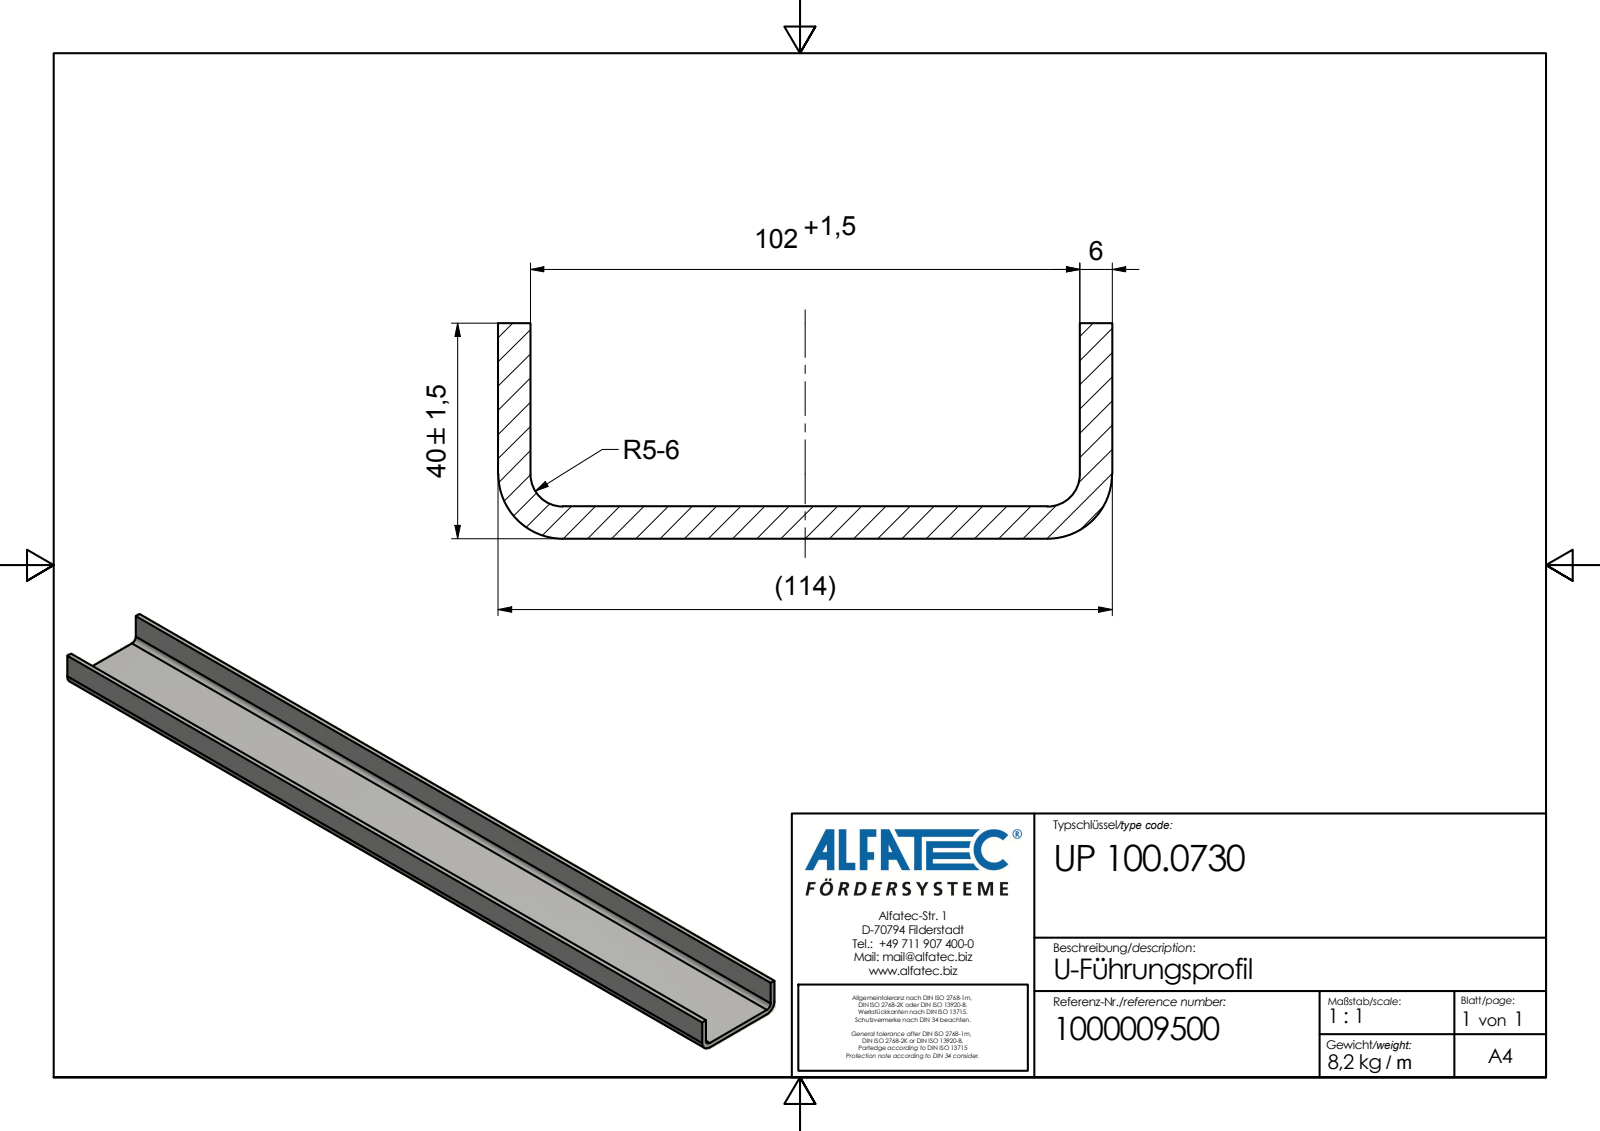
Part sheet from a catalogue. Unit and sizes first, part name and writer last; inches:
Units: inches
Overall size (bounding box): 39.37 × 4.488 × 1.575
Partial cylindrical surfaces — rounded edges, fillets, slot ends (radius × count): R0.236 ×2, R0.472 ×2
Main face-to-face distances: 0.236, 4.252, 4.016, 4.488, 1.575, 1.339, 39.37
Volume: 63.83 in³ · Surface area: 562.1 in²
Bodies: 1 solid, 14 faces (10 planar, 4 cylindrical, 0 other)
Part name (STEP PRODUCT): UP 100.0730
STEP written by: Autodesk Inventor 2020 (AUTOMOTIVE_DESIGN)
